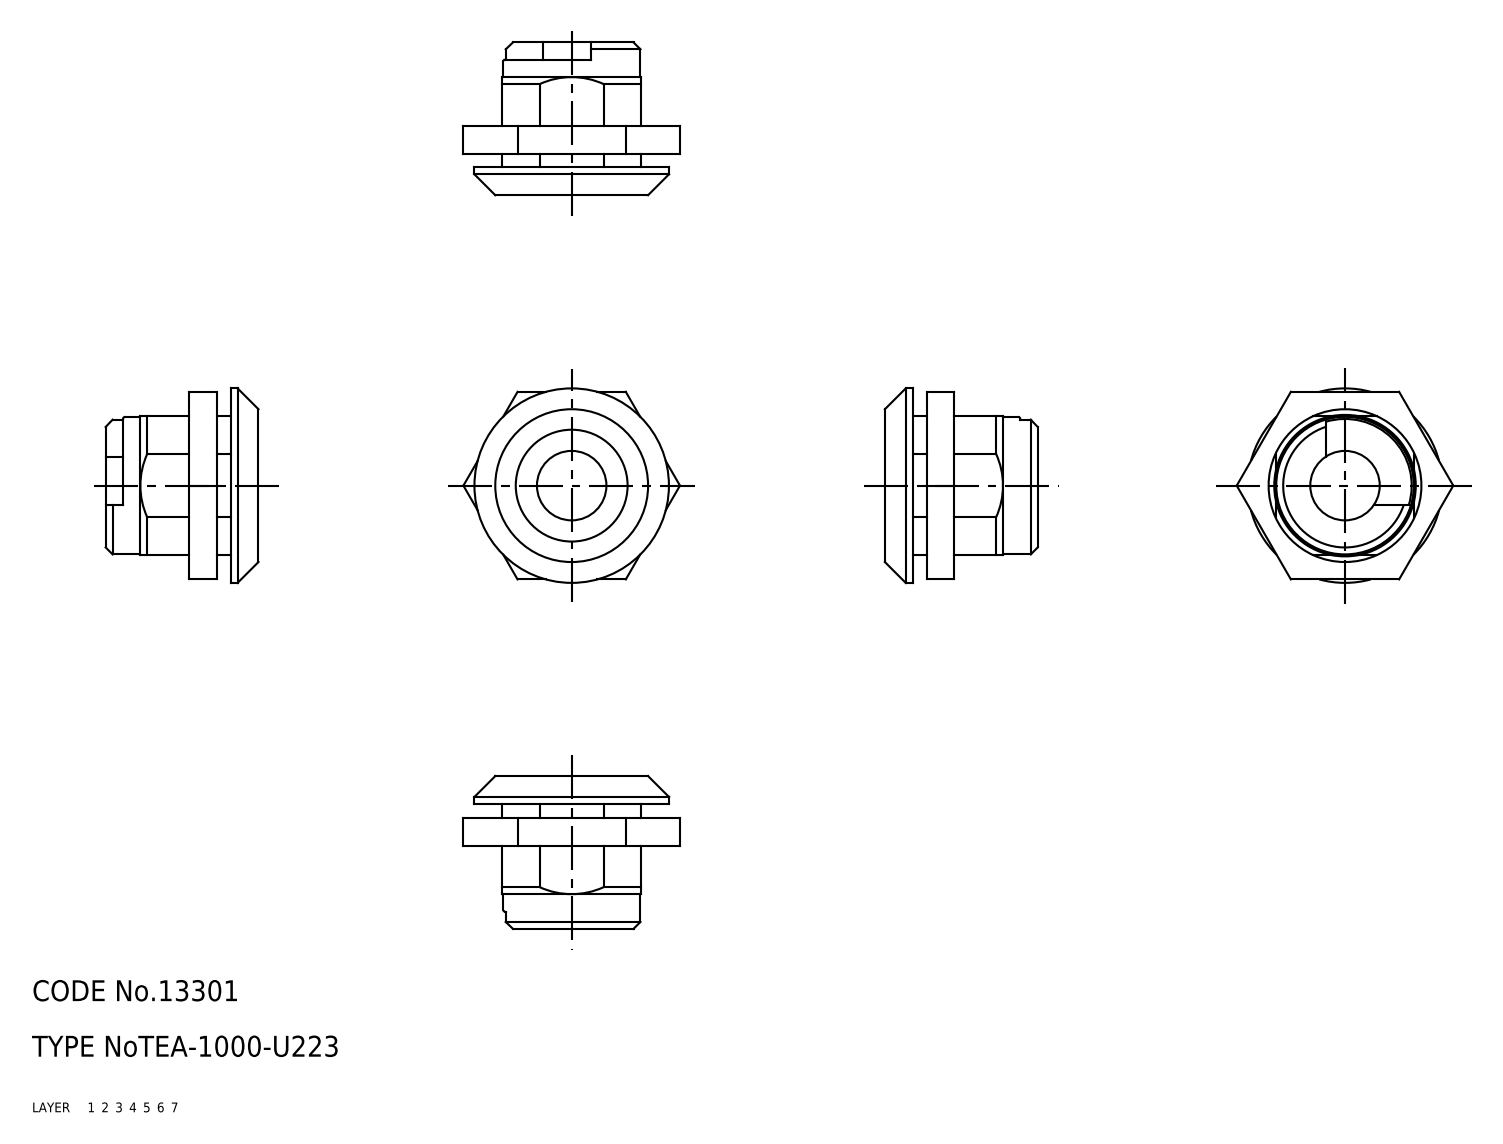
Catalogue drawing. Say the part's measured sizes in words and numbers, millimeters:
The part is named "nut; housing; TEA_1000_U223_9009_36". Its 3-D file was written by "CADfix (AUTOMOTIVE_DESIGN)". It is 2 solids with 42 faces: 0 planar, 0 cylindrical and 42 other. Overall it measures 31.18 by 28 by 22 millimeters. Its volume is 5 345 cubic millimeters and its surface area 4 479 square millimeters.
